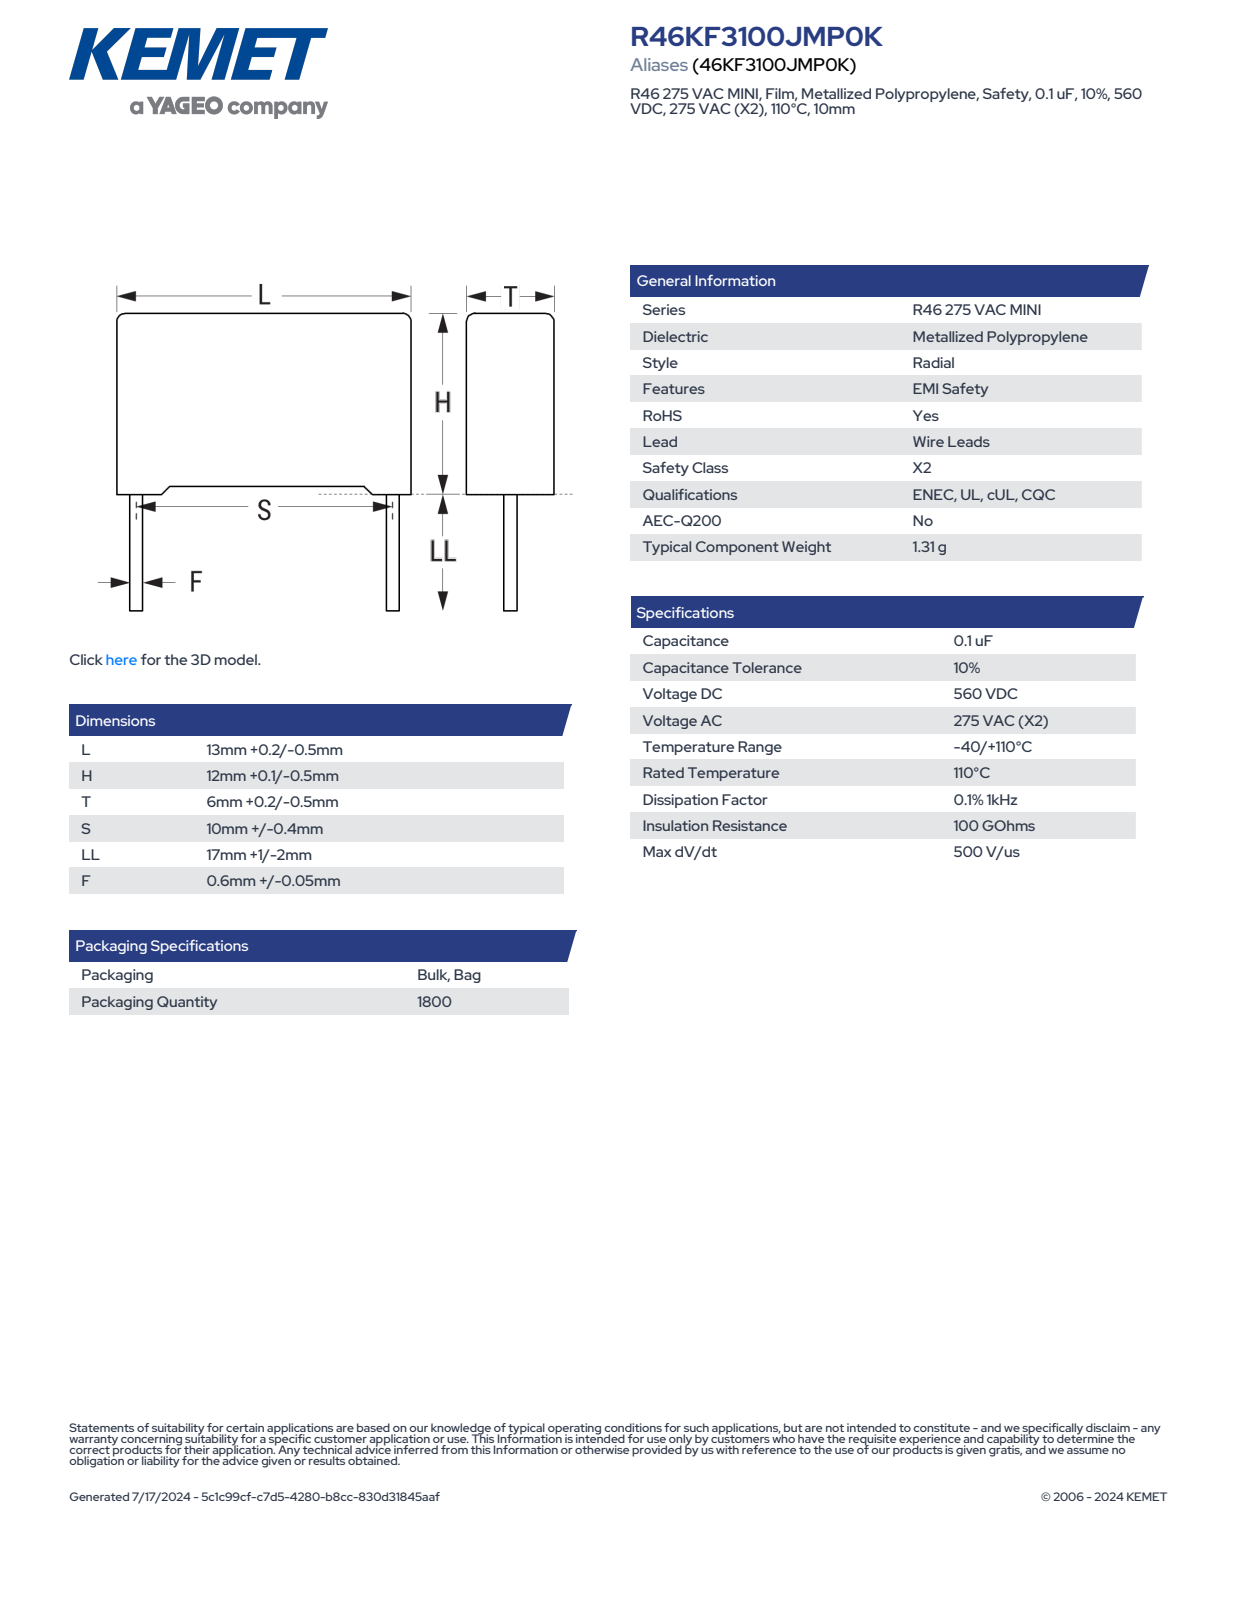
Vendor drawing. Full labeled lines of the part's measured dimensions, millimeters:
Part name (STEP PRODUCT): CFR_RB2_13X12X6_L13.2H12.1T6.2S10LL18F0.65
STEP written by: SolidWorks 2021 (AUTOMOTIVE_DESIGN)
Units: millimetres
Bodies: 4 solids, 85 faces (77 planar, 8 cylindrical, 0 other)
Overall size (bounding box): 30.1 × 13.2 × 6.21
Volume: 949 mm³ · Surface area: 730 mm²
Round bosses / shafts (diameter × count): ⌀0.65 ×2
Partial cylindrical surfaces — rounded edges, fillets, slot ends (radius × count): R0.5 ×4
Main face-to-face distances: 6.2, 13.2, 11.35, 0.44, 5.76, 0.75, 12.1, 12.76, 5.32, 0.42
